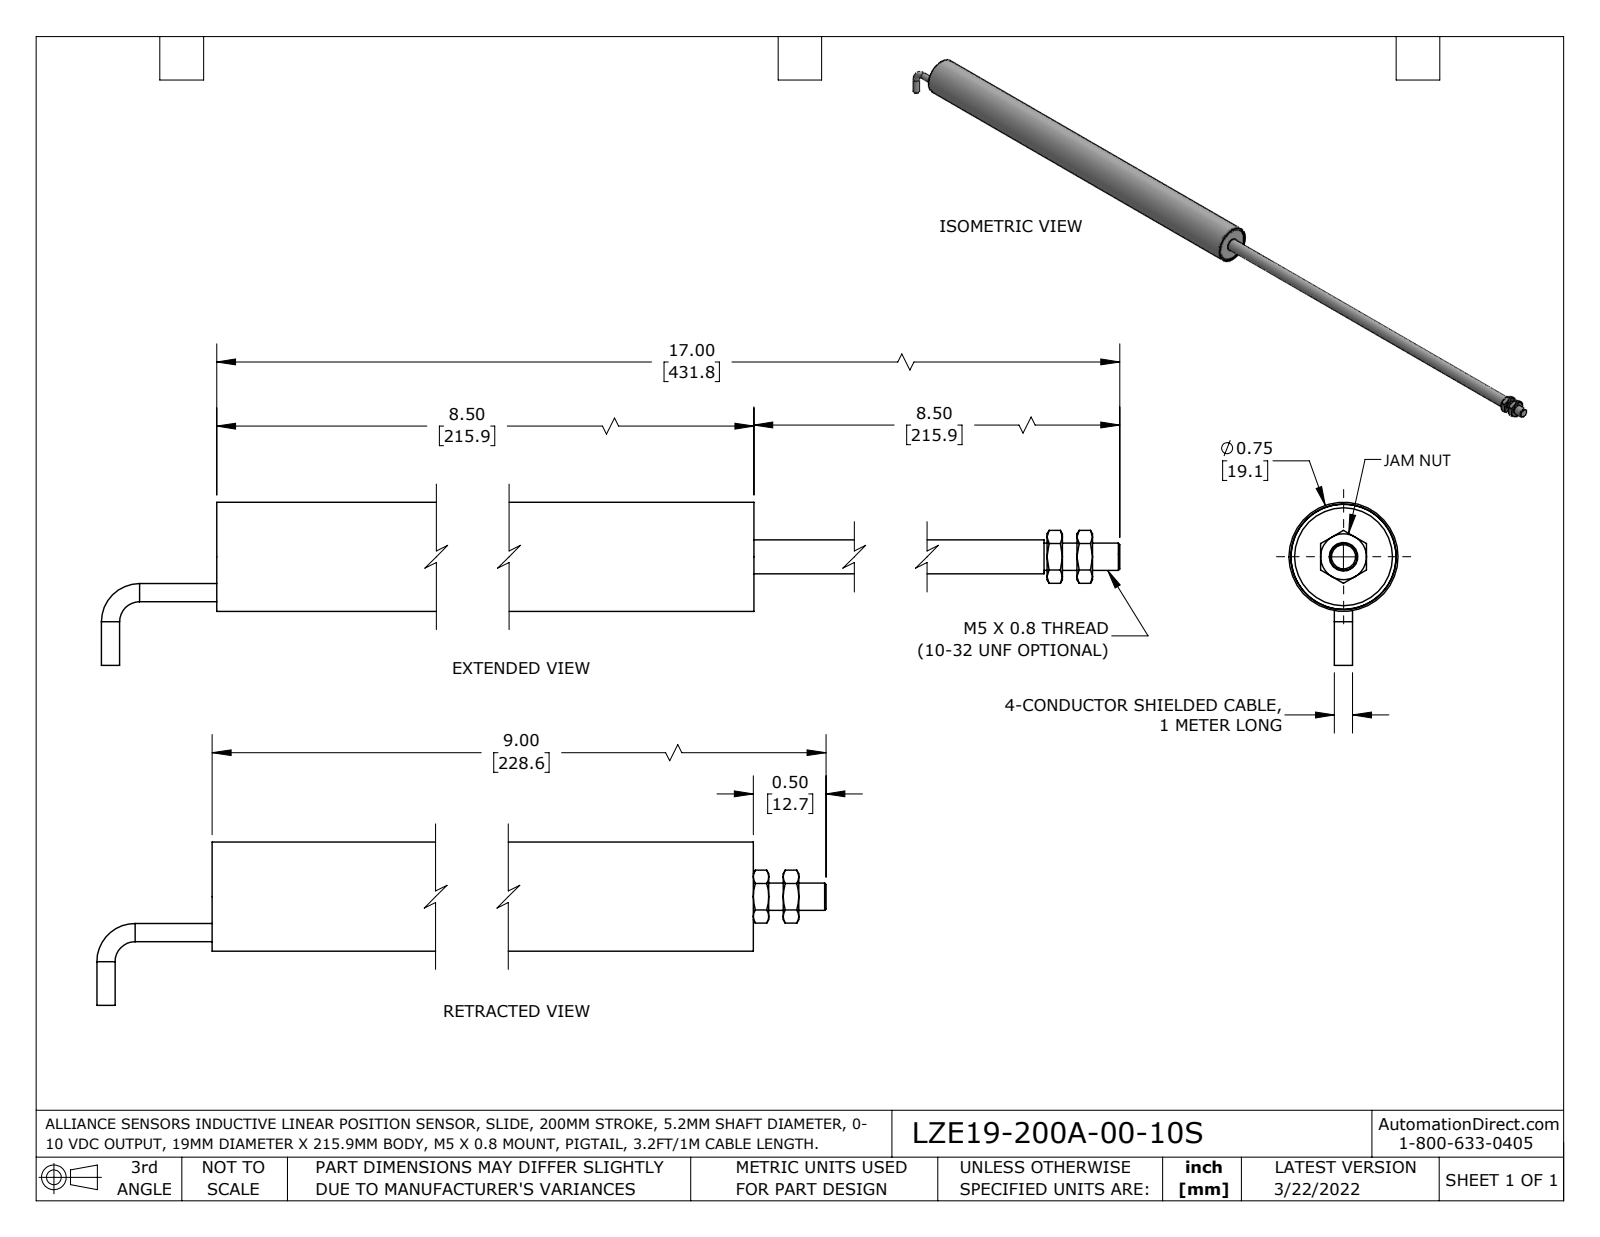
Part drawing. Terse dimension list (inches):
name: 5500-0031; 5300-0002; 3120-0007-ZY_with slot; 3120-0008-06_-08 (+6 more)
written by: SolidWorks 2021 (AUTOMOTIVE_DESIGN)
unit: in
bodies: 10 solids, 137 faces (42 planar, 44 cylindrical, 51 other)
size: 17.793 × 1.121 × 0.75
volume: 1.29 in³; area: 72.52 in²
holes: 1× ⌀0.165, 1× ⌀0.188, 1× ⌀0.197, 1× ⌀0.234, 1× ⌀0.281, 1× ⌀0.68, 1× ⌀0.725
bosses: 2× ⌀0.125, 1× ⌀0.75, 1× ⌀0.723, 1× ⌀0.278, 1× ⌀0.187
rounds: 1× R0.052
face distances: 0.06, 8.42, 0.08, 8.36, 8.48, 0.315, 0.206, 0.106, 0.374, 8.5
